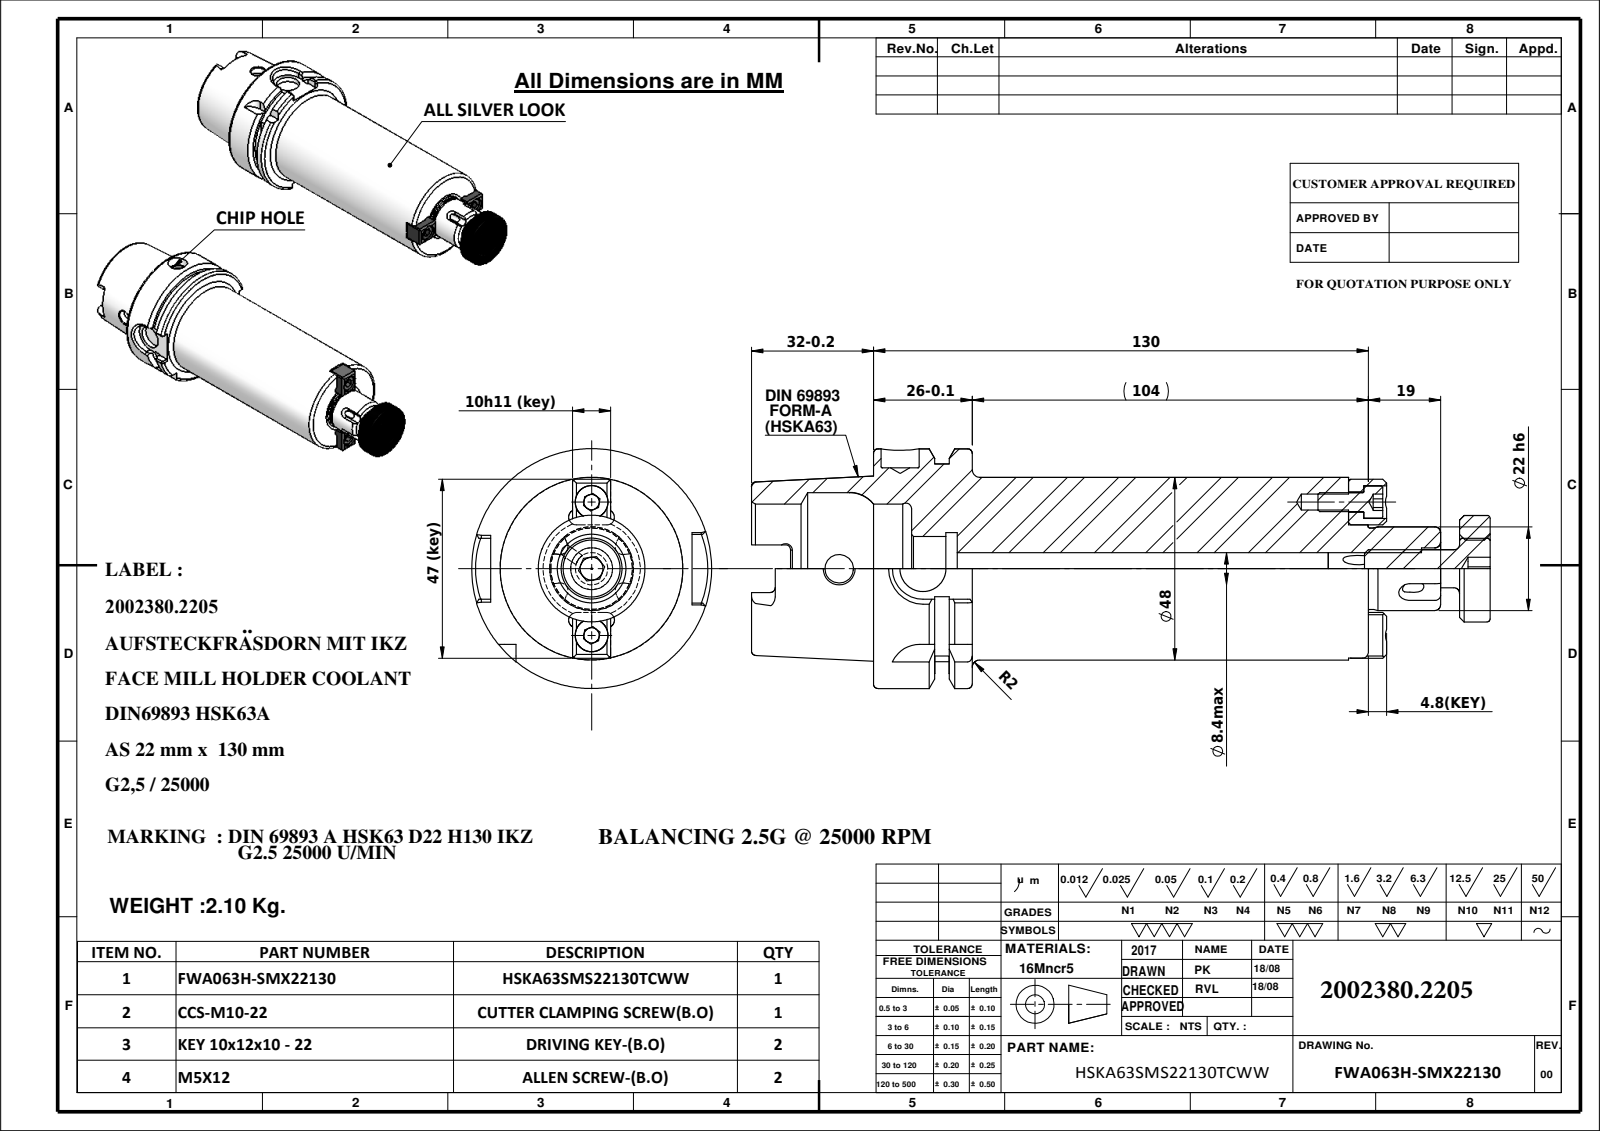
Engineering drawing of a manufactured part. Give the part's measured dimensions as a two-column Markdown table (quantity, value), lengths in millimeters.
| quantity | value |
| --- | --- |
| part name | 9163A-AS522130; CCS-M10-22-1 LONG; M5X12_DIN 912 M5 x 12 --- 12N; CCS-M10-22-2 (+4 more) |
| STEP written by | SolidWorks 2009 (CONFIG_CONTROL_DESIGN) |
| units | millimeters |
| bodies | 7 solids, 394 faces (165 planar, 101 cylindrical, 128 other) |
| overall size | 194 × 63 × 63 |
| volume | 275 660 mm³ |
| surface area | 49 453 mm² |
| round holes (diameter × count) | 3 × 4, 4.2 × 2, 5.4 × 2, 8.6 × 2, 7.5 × 1, 8.4 × 1, 8.5 × 1, 10 × 1, 11 × 1, 12 × 1, 15 × 1, 17 × 1 |
| round bosses / shafts (diameter × count) | 8.5 × 2, 5 × 2, 63 × 1, 55 × 1, 48 × 1, 28 × 1, 22 × 1, 21.4 × 1 |
| partial cylindrical surfaces (radius × count) | 2 × 8, 1.3 × 6, 2.88 × 4, 8 × 2, 9 × 1 |
| main face-to-face distances | 130, 32, 162, 10, 25.95, 104.05, 15.95, 120, 152, 136.05 |
| hole center spacings | 17.5, 22, 35 |
